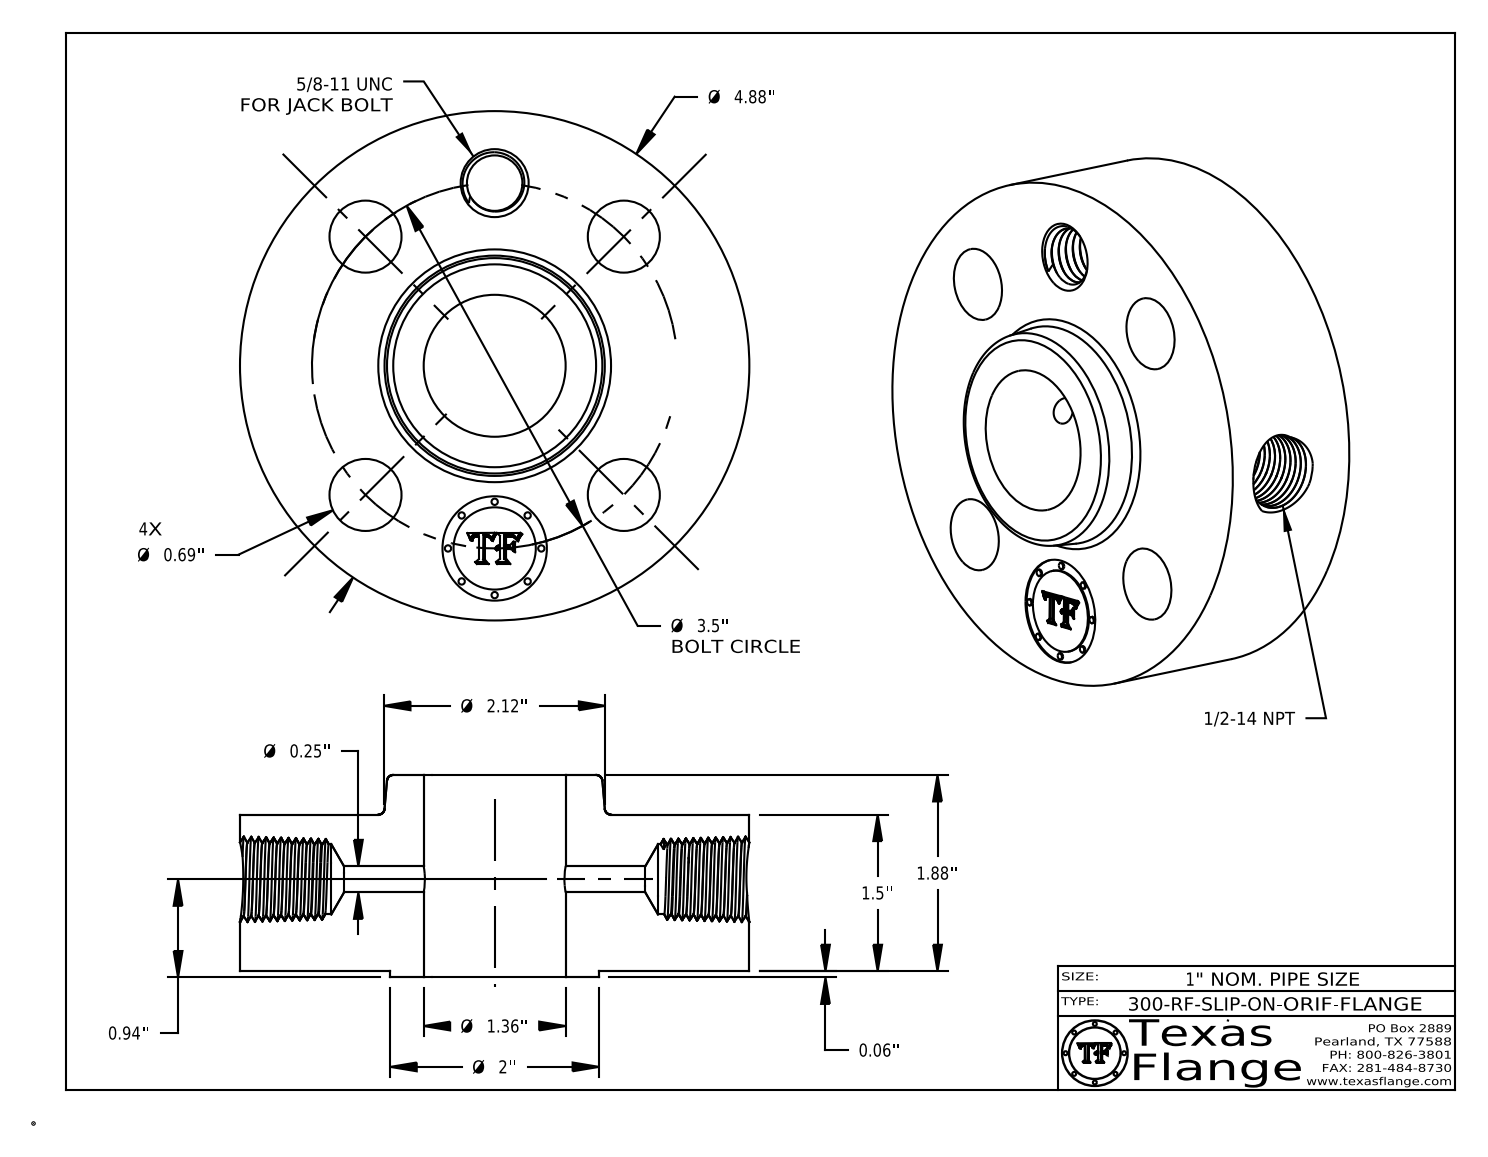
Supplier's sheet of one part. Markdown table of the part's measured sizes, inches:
| quantity | value |
| --- | --- |
| part name | 300-RF-SLIP-ON |
| STEP written by | CATIA V5 STEP AP214 (AUTOMOTIVE_DESIGN) |
| units | inches |
| bodies | 1 solid, 762 faces (369 planar, 85 cylindrical, 308 other) |
| overall size | 4.88 × 4.88 × 1.94 |
| volume | 23.23 in³ |
| surface area | 89.72 in² |
| round holes (diameter × count) | 0.69 × 4, 0.25 × 1, 0.531 × 1, 0.672 × 1, 1 × 1, 1.36 × 1 |
| round bosses / shafts (diameter × count) | 0.061 × 8, 4.88 × 1, 2 × 1, 0.788 × 1 |
| main face-to-face distances | 1.5, 0.06, 1.56, 1.94, 1.88, 0.38, 1.545, 1.485, 0.015, 0.395 |
| hole center spacings | 1.75, 1.339, 2.475, 3.233, 3.5 |
